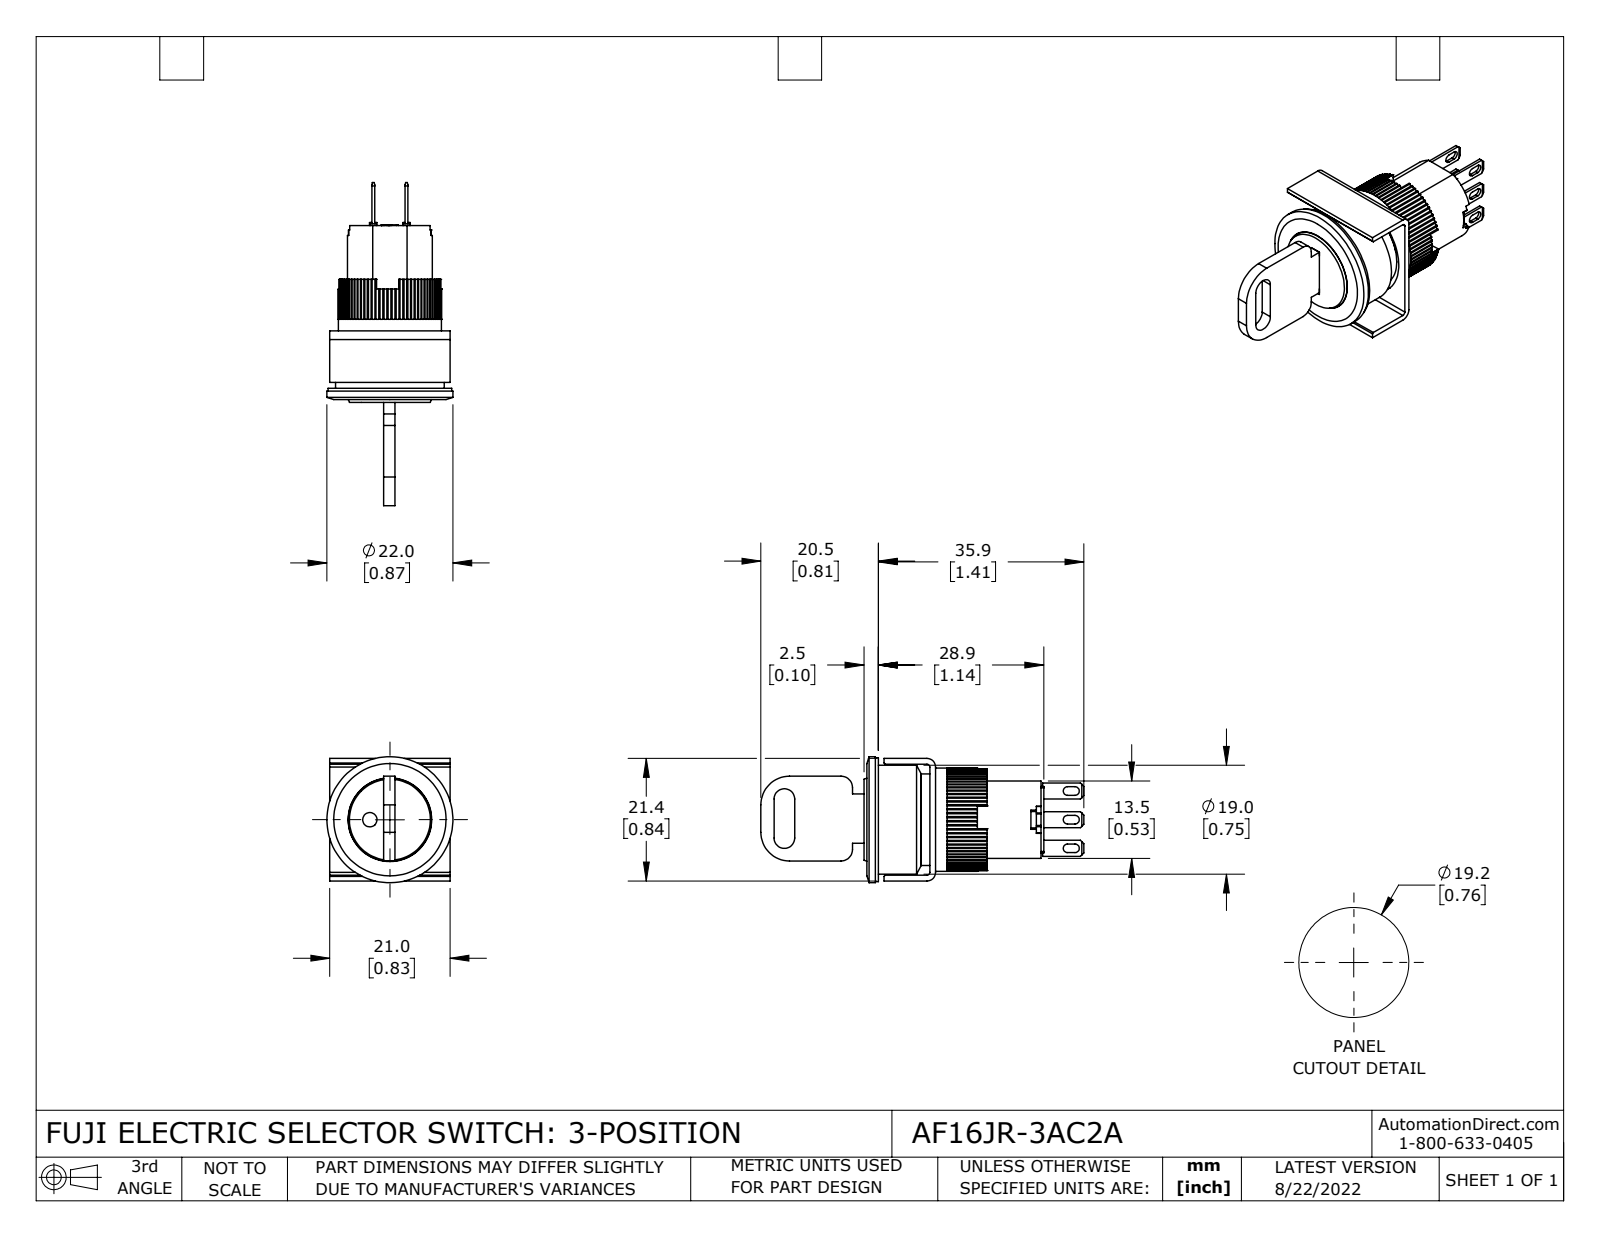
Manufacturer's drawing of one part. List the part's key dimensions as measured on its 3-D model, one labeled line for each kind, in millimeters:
Part name (STEP PRODUCT): AF16JR-3AC2A
STEP written by: SolidWorks 2021 (CONFIG_CONTROL_DESIGN)
Units: millimetres
Bodies: 13 solids, 707 faces (518 planar, 183 cylindrical, 6 other)
Overall size (bounding box): 56.4 × 22 × 22
Volume: 8 110 mm³ · Surface area: 7 252 mm²
Round holes (diameter × count): ⌀1 ×1, ⌀2.5 ×1, ⌀14.6 ×1, ⌀18 ×1, ⌀19 ×1
Round bosses / shafts (diameter × count): ⌀22 ×1, ⌀21.6 ×1, ⌀16 ×1, ⌀14.8 ×1, ⌀14.5 ×1
Partial cylindrical surfaces — rounded edges, fillets, slot ends (radius × count): R0.3 ×80, R0.2 ×12, R0.8 ×6, R0.5 ×2, R1.5 ×2, R1.8 ×2, R2 ×2, R5 ×2
Main face-to-face distances: 2, 1, 0.5, 9.5, 4.5, 2.5, 10, 20.4, 1.5, 19.4
Hole centre spacings: 3.5
